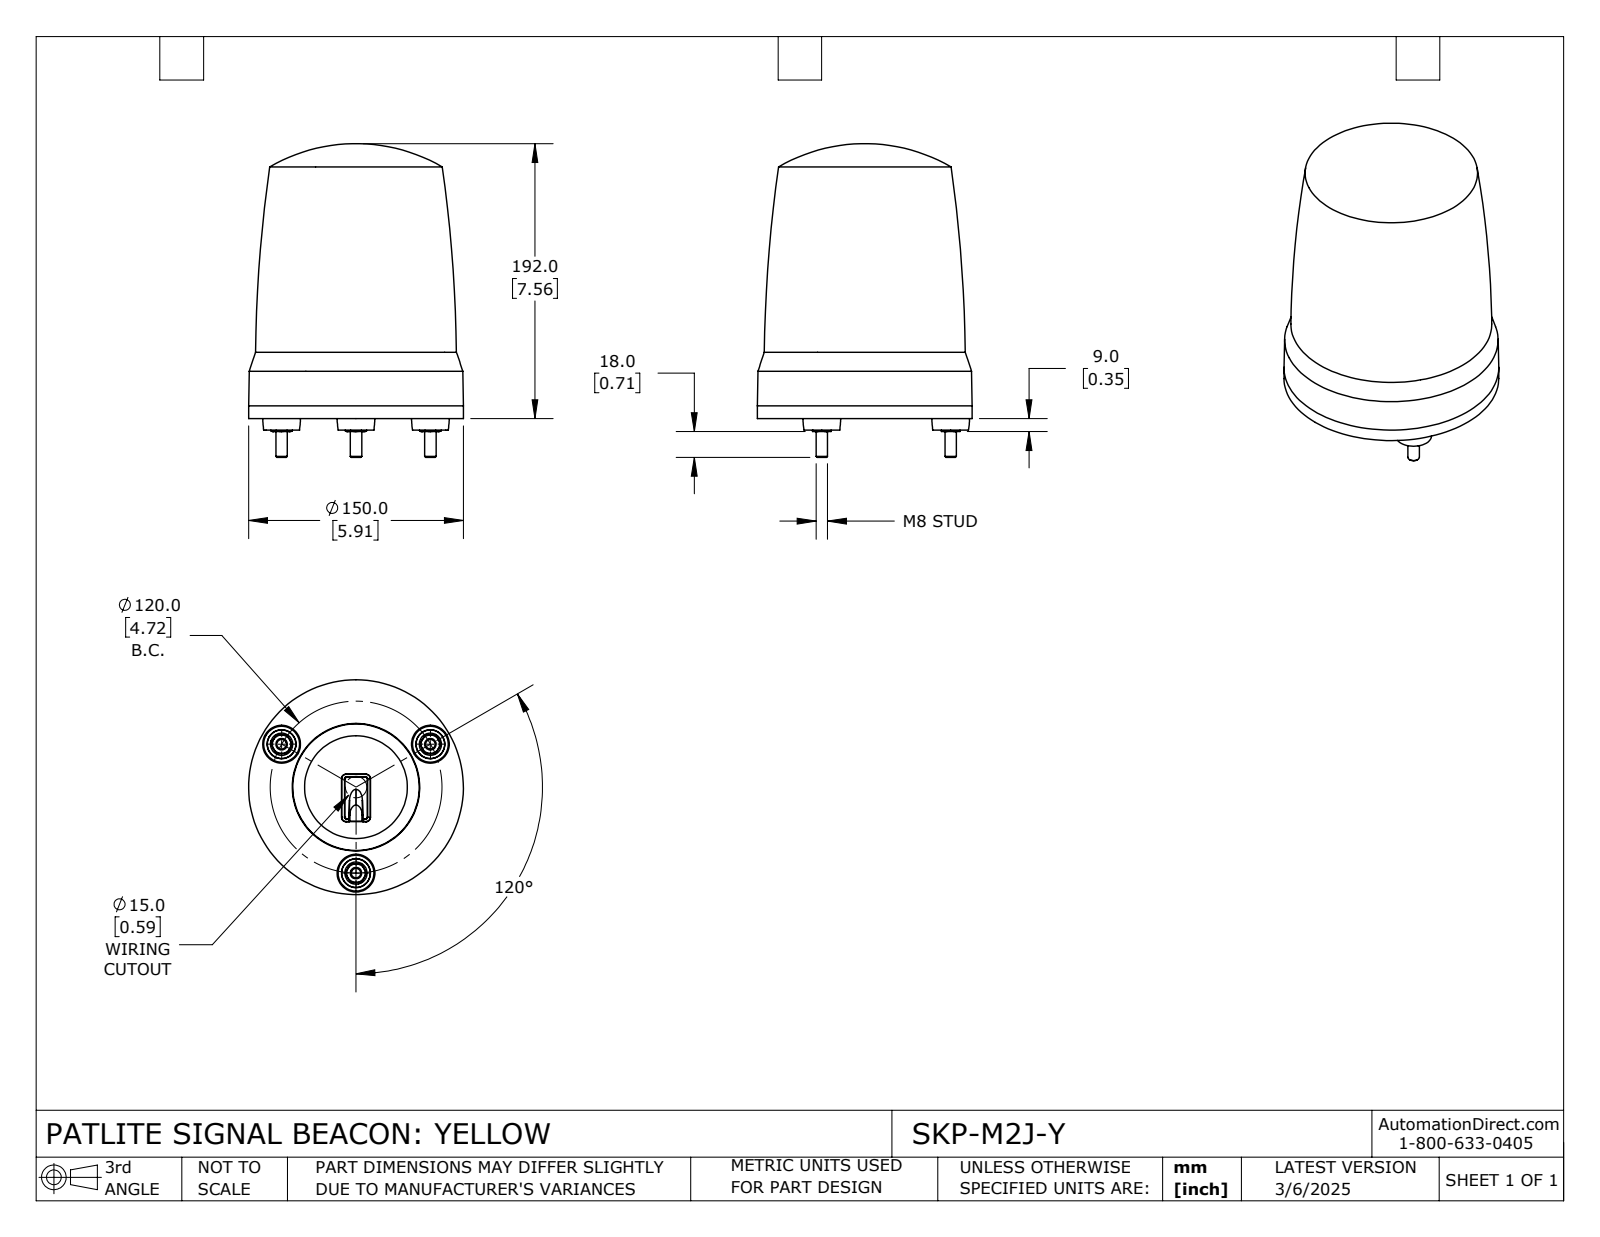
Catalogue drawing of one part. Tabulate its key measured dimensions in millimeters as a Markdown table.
| quantity | value |
| --- | --- |
| part name | SKP-M2J-Y |
| STEP written by | SolidWorks 2024 (CONFIG_CONTROL_DESIGN) |
| units | millimeters |
| bodies | 1 solid, 144 faces (49 planar, 14 cylindrical, 81 other) |
| overall size | 219 × 150 × 150 |
| volume | 2 538 000 mm³ |
| surface area | 119 026 mm² |
| round bosses / shafts (diameter × count) | 15.5 × 3, 8 × 3, 150 × 1 |
| main face-to-face distances | 32.7, 8, 40.7, 13, 7.1, 0.9, 33.6, 1.6, 36.05, 41.55 |
